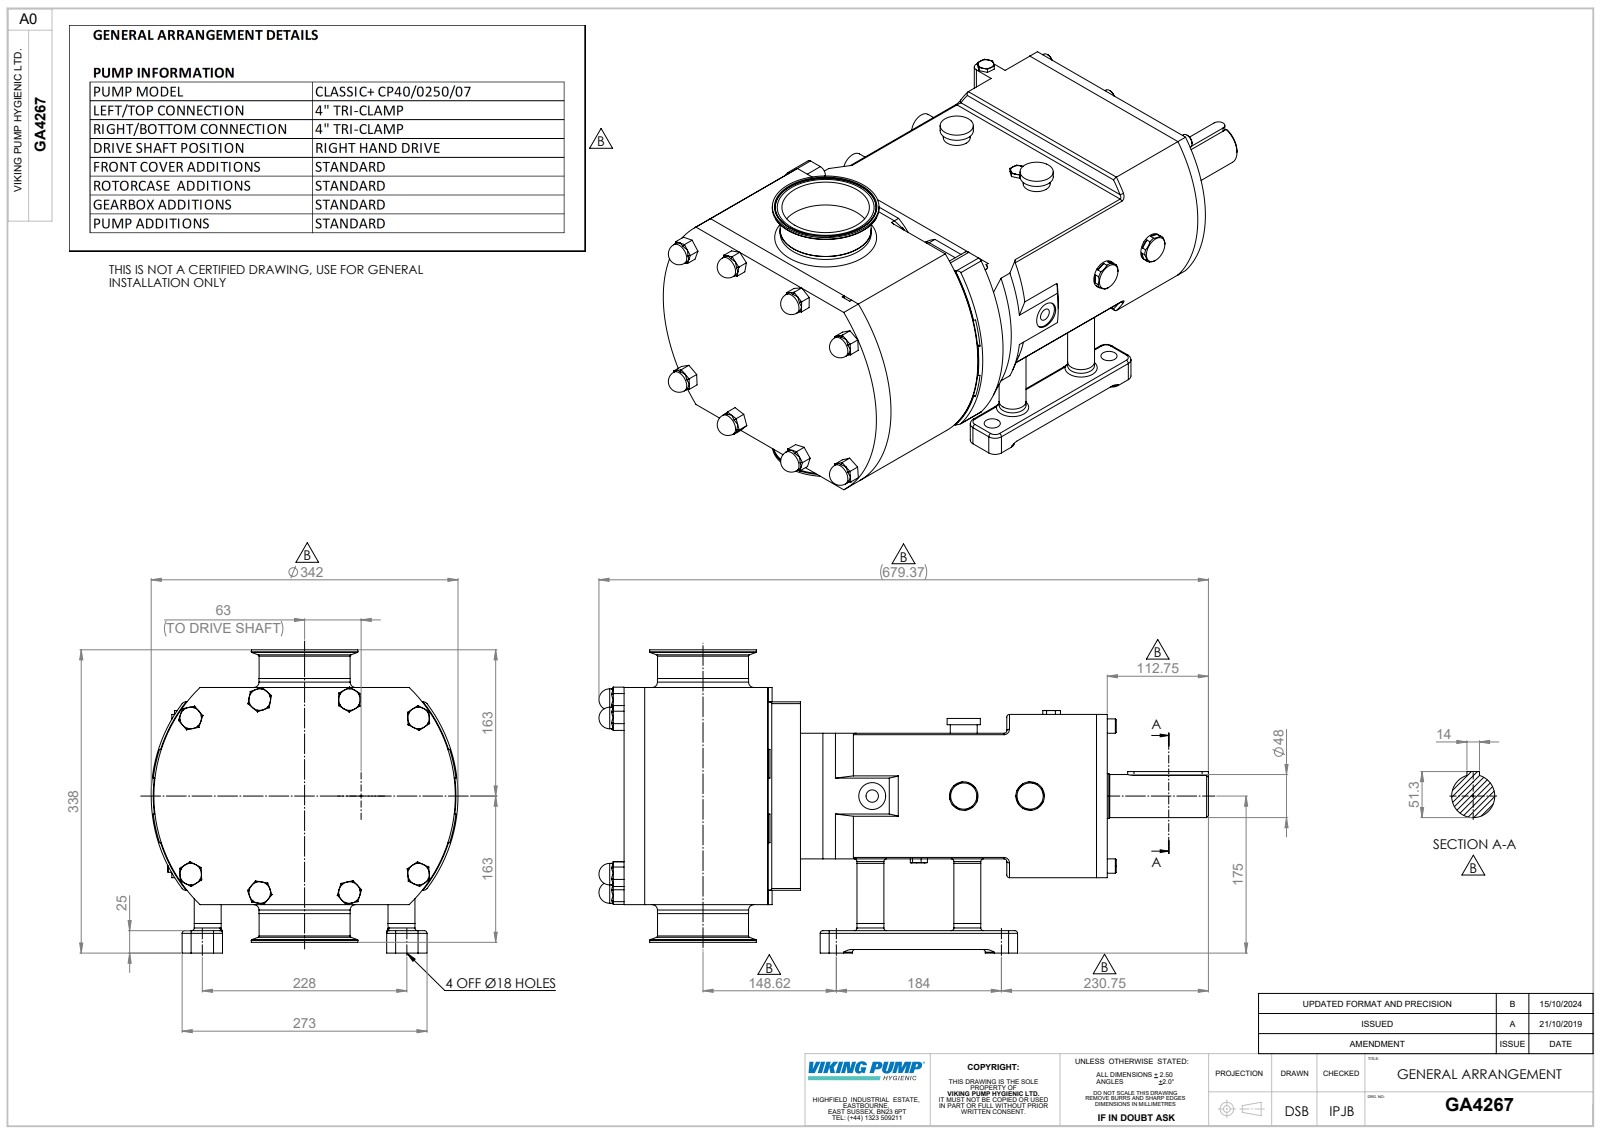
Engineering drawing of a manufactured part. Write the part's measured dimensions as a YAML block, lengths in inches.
part_name: "Copy of CP40L-0250 V RHD^GA4267; Copy of Z94-5121-66 - 4 INCH^GA4267; GA4267"
step_written_by: "SolidWorks 2023 (AUTOMOTIVE_DESIGN)"
units: inches
bodies: {solids: 3, faces: 965, planar: 365, cylindrical: 279, other: 321}
overall_size: [26.747, 13.465, 13.307]
volume: 1764
surface_area: 1518
round_holes:
  - {diameter: 0.402, count: 4}
  - {diameter: 0.709, count: 4}
  - {diameter: 0.468, count: 2}
  - {diameter: 1.378, count: 2}
  - {diameter: 0.544, count: 1}
  - {diameter: 1.181, count: 1}
  - {diameter: 3.839, count: 1}
round_bosses_or_shafts:
  - {diameter: 1.181, count: 10}
  - {diameter: 0.945, count: 8}
  - {diameter: 0.63, count: 6}
  - {diameter: 4.331, count: 2}
  - {diameter: 2.756, count: 2}
  - {diameter: 1.457, count: 2}
  - {diameter: 1.25, count: 2}
  - {diameter: 9.843, count: 1}
partial_cylinders:
  - {radius: 0.394, count: 24}
  - {radius: 0.118, count: 22}
  - {radius: 0.315, count: 20}
  - {radius: 0.236, count: 10}
  - {radius: 0.197, count: 4}
  - {radius: 0.433, count: 4}
  - {radius: 0.276, count: 2}
  - {radius: 0.6, count: 2}
face_to_face_distances: [0.827, 2.008, 7.52, 1.181, 8.346, 6.339, 5.512, 21.206, 9.528, 7.165]
hole_center_spacings: [4.252, 2.128, 3.074, 4.309, 4.683, 4.961, 6.013, 7.244]
